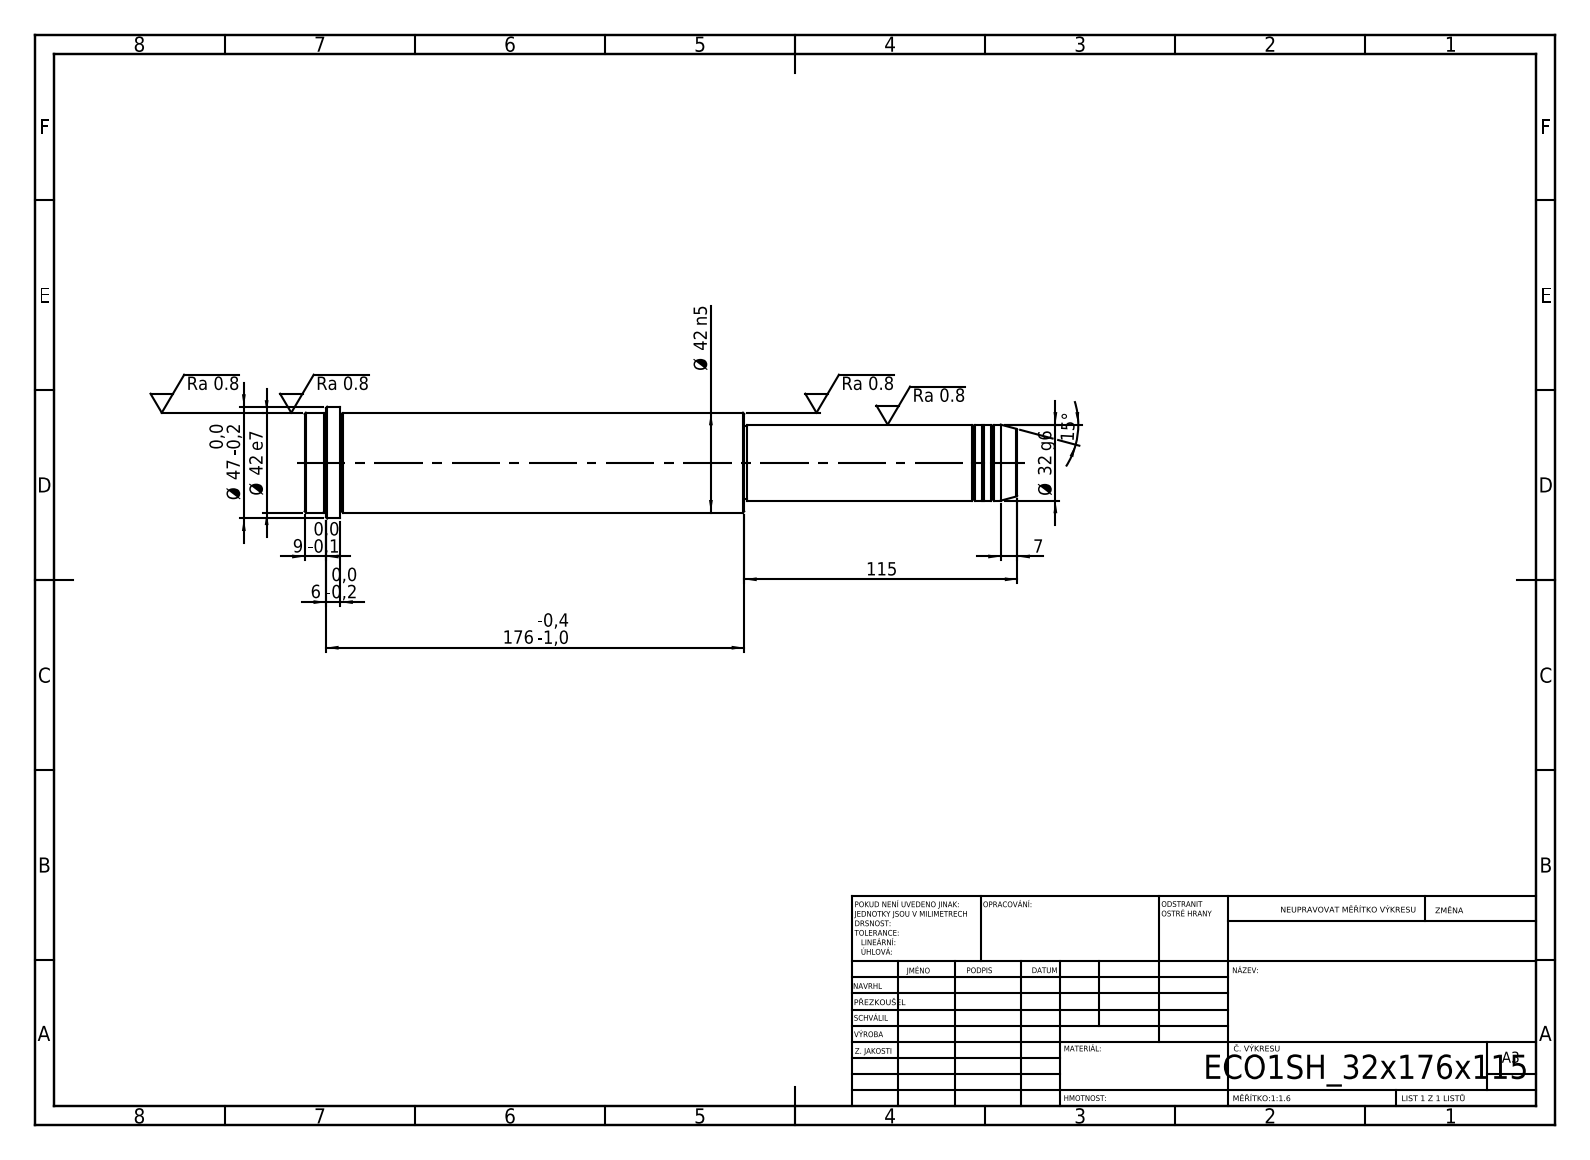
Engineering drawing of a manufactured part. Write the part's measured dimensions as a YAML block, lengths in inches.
step_written_by: "SolidWorks 2019 (CONFIG_CONTROL_DESIGN)"
units: inches
bodies: {solids: 1, faces: 52, planar: 6, cylindrical: 16, other: 30}
overall_size: [11.811, 1.85, 1.85]
volume: 21.35
surface_area: 61.4
round_bosses_or_shafts:
  - {diameter: 1.85, count: 1}
  - {diameter: 1.654, count: 1}
  - {diameter: 1.26, count: 1}
  - {diameter: 1.22, count: 1}
face_to_face_distances: [11.811, 4.528, 7.283, 11.22, 6.693, 0.591, 11.457, 6.929, 0.236, 0.354]
